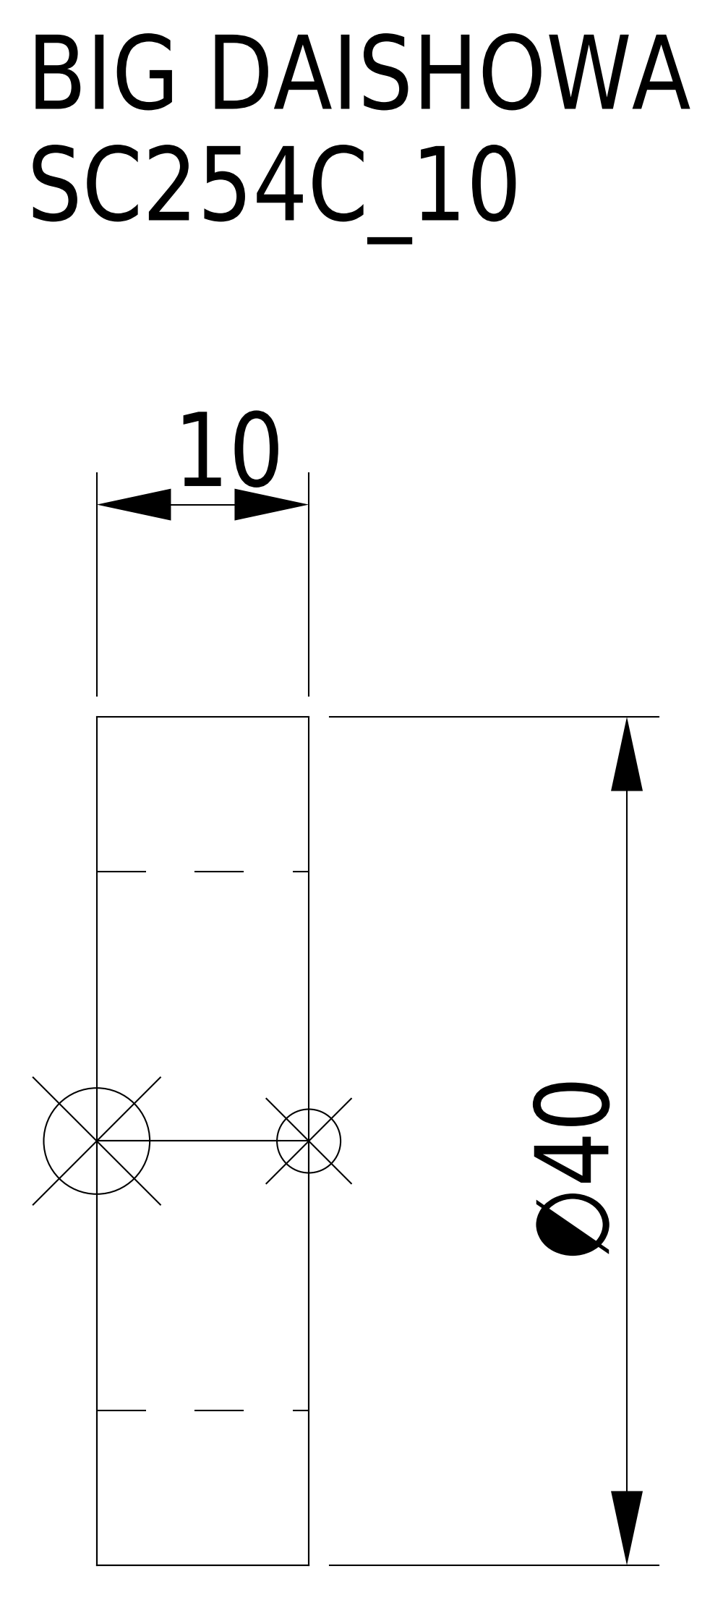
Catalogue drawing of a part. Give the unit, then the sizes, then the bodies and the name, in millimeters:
Units: millimetres
Overall size (bounding box): 40 × 40 × 10
Round holes (diameter × count): ⌀25.4 ×1
Round bosses / shafts (diameter × count): ⌀40 ×1
Main face-to-face distances: 10, 6.5
Volume: 7 315 mm³ · Surface area: 3 579 mm²
Bodies: 1 solid, 8 faces (5 planar, 3 cylindrical, 0 other)
Part name (STEP PRODUCT): SC254C_10
STEP written by: CREO PARAMETRIC BY PTC INC, 2016380 (AUTOMOTIVE_DESIGN)
